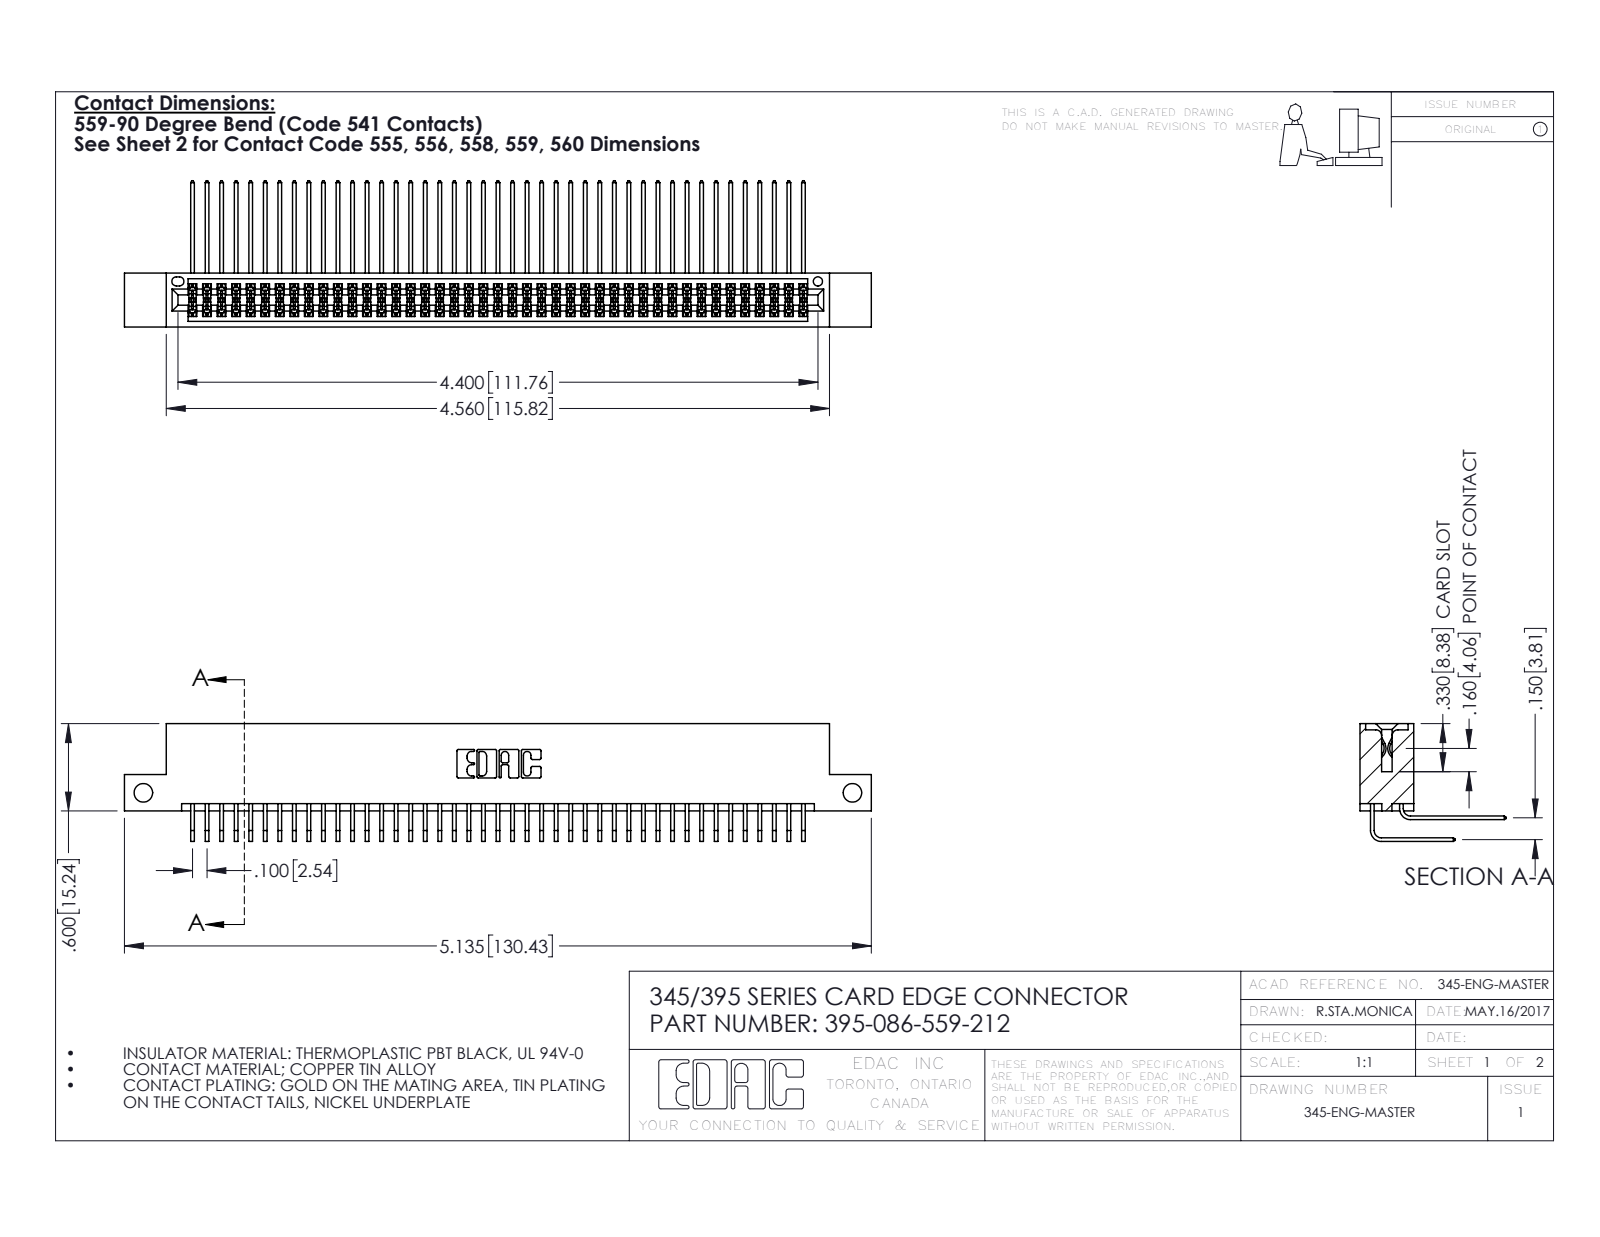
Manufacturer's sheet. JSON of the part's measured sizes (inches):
{"part_name": "395-086-559-212; 345-292-001_558 559 Tail - 1; 345-292-001_559 Tail - 2; 345 Part_Flush Mounting Lugs - Side Mount", "step_written_by": "SolidWorks 2016 (CONFIG_CONTROL_DESIGN)", "units": "inches", "bodies": {"solids": 87, "faces": 4598, "planar": 3090, "cylindrical": 1508, "other": 0}, "overall_size": [5.135, 1.005, 0.809], "volume_in3": 0.799, "surface_area_in2": 33.42, "round_holes": [[0.128, 2], [0.064, 1]], "partial_cylinders_radius": [[0.006, 130], [0.01, 22], [0.007, 6], [0.031, 6], [0.026, 3], [0.014, 2], [0.019, 2], [0.022, 2]], "face_to_face_distances": [0.072, 0.298, 0.2, 0.37, 0.098, 0.272, 0.025, 0.225, 0.175, 0.15], "hole_center_spacings": [4.875]}
